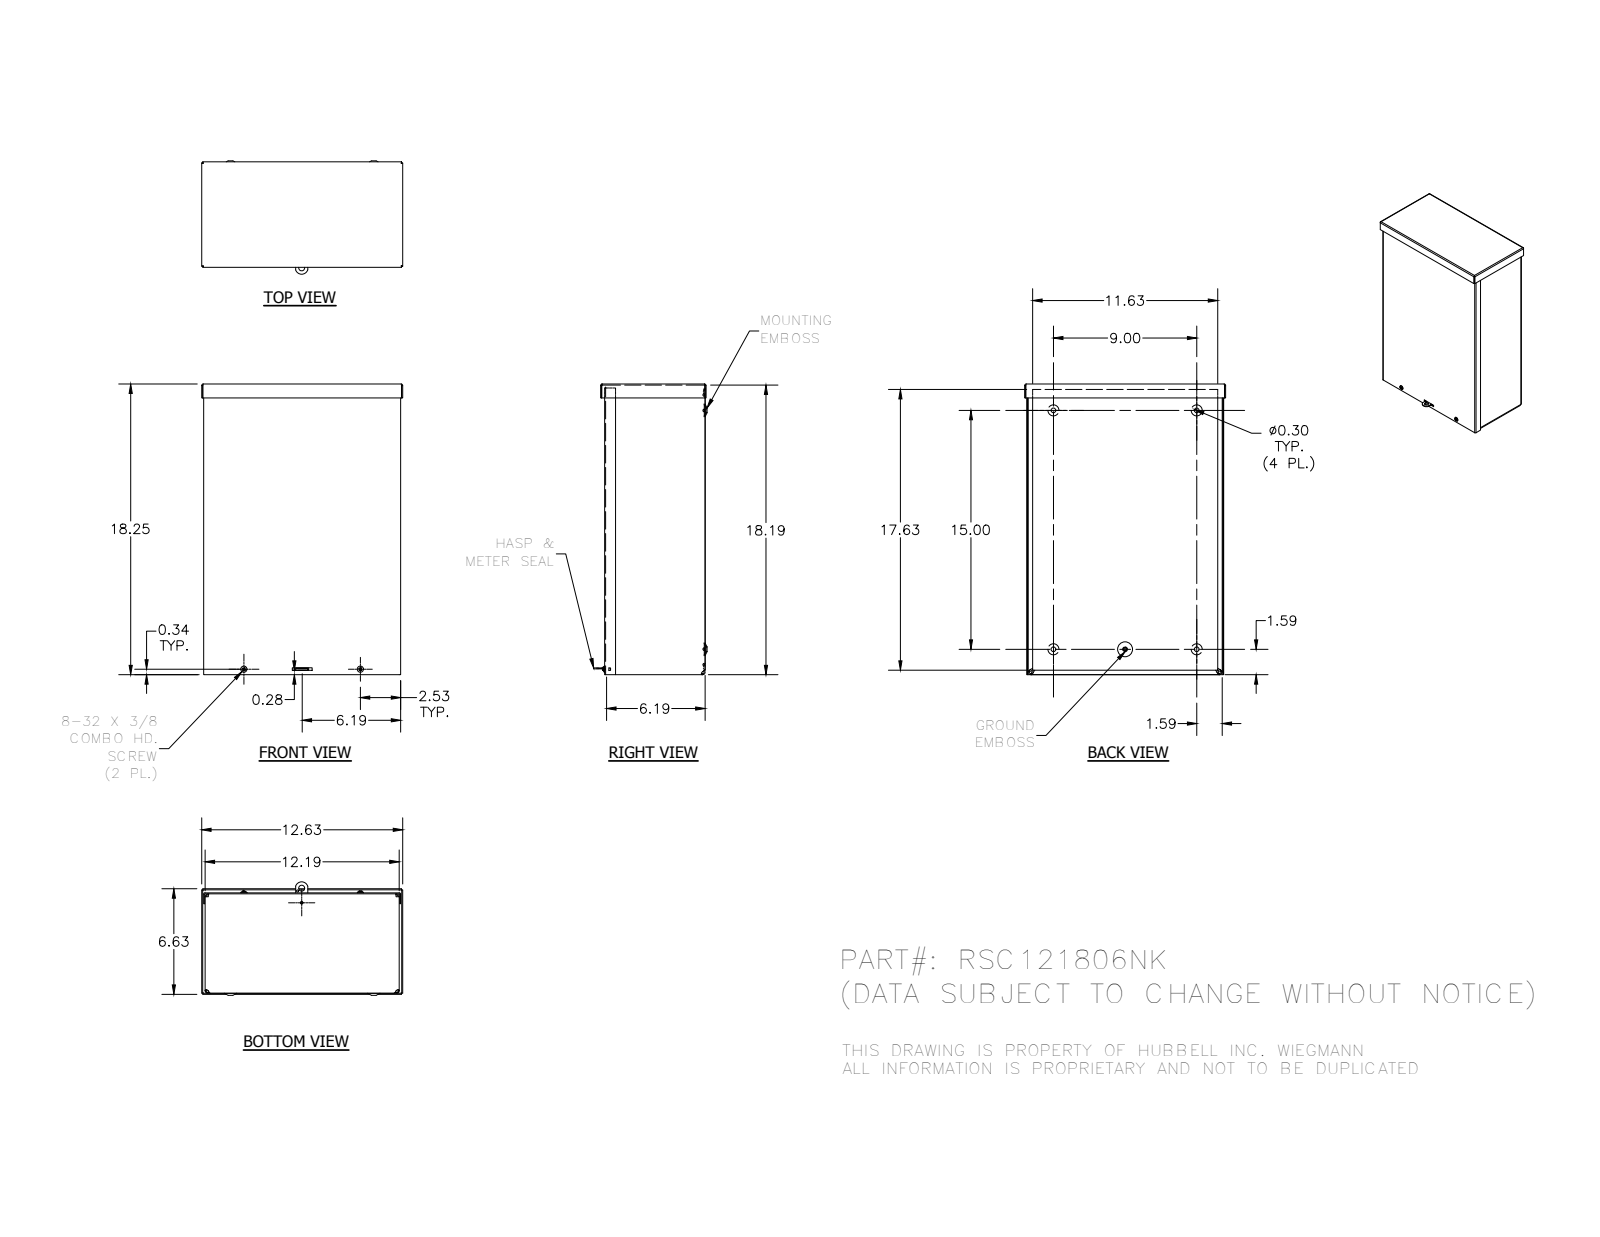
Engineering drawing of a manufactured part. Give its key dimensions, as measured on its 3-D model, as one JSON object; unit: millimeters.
{"part_name": "RSC121806NK_WRAP; RSC1218NK_LID; RSC1206NK_CAP; 3183 (+3 more)", "step_written_by": "Autodesk Inventor 2014 (AUTOMOTIVE_DESIGN)", "units": "millimeters", "bodies": {"solids": 7, "faces": 377, "planar": 163, "cylindrical": 78, "other": 136}, "overall_size": [463.56, 320.68, 180.97], "volume_mm3": 1040000, "surface_area_mm2": 1332000, "round_holes": [[7.62, 4], [7.95, 4], [3.76, 2], [3.17, 1], [3.45, 1], [3.96, 1], [4.19, 1], [9.52, 1]], "round_bosses_or_shafts": [[9.75, 2], [4.17, 2], [5.8, 1]], "partial_cylinders_radius": [[0.79, 8], [2.37, 8], [3.17, 8], [4.75, 8], [1.4, 4], [1.57, 4], [2.38, 4], [2.97, 4]], "face_to_face_distances": [1.58, 158.73, 157.15, 1.57, 307.99, 1.59, 160.32, 158.74, 460.39, 3.15], "hole_center_spacings": [34.43, 114.3, 185.75, 228.6, 381, 397.77, 408.51, 413.34]}
